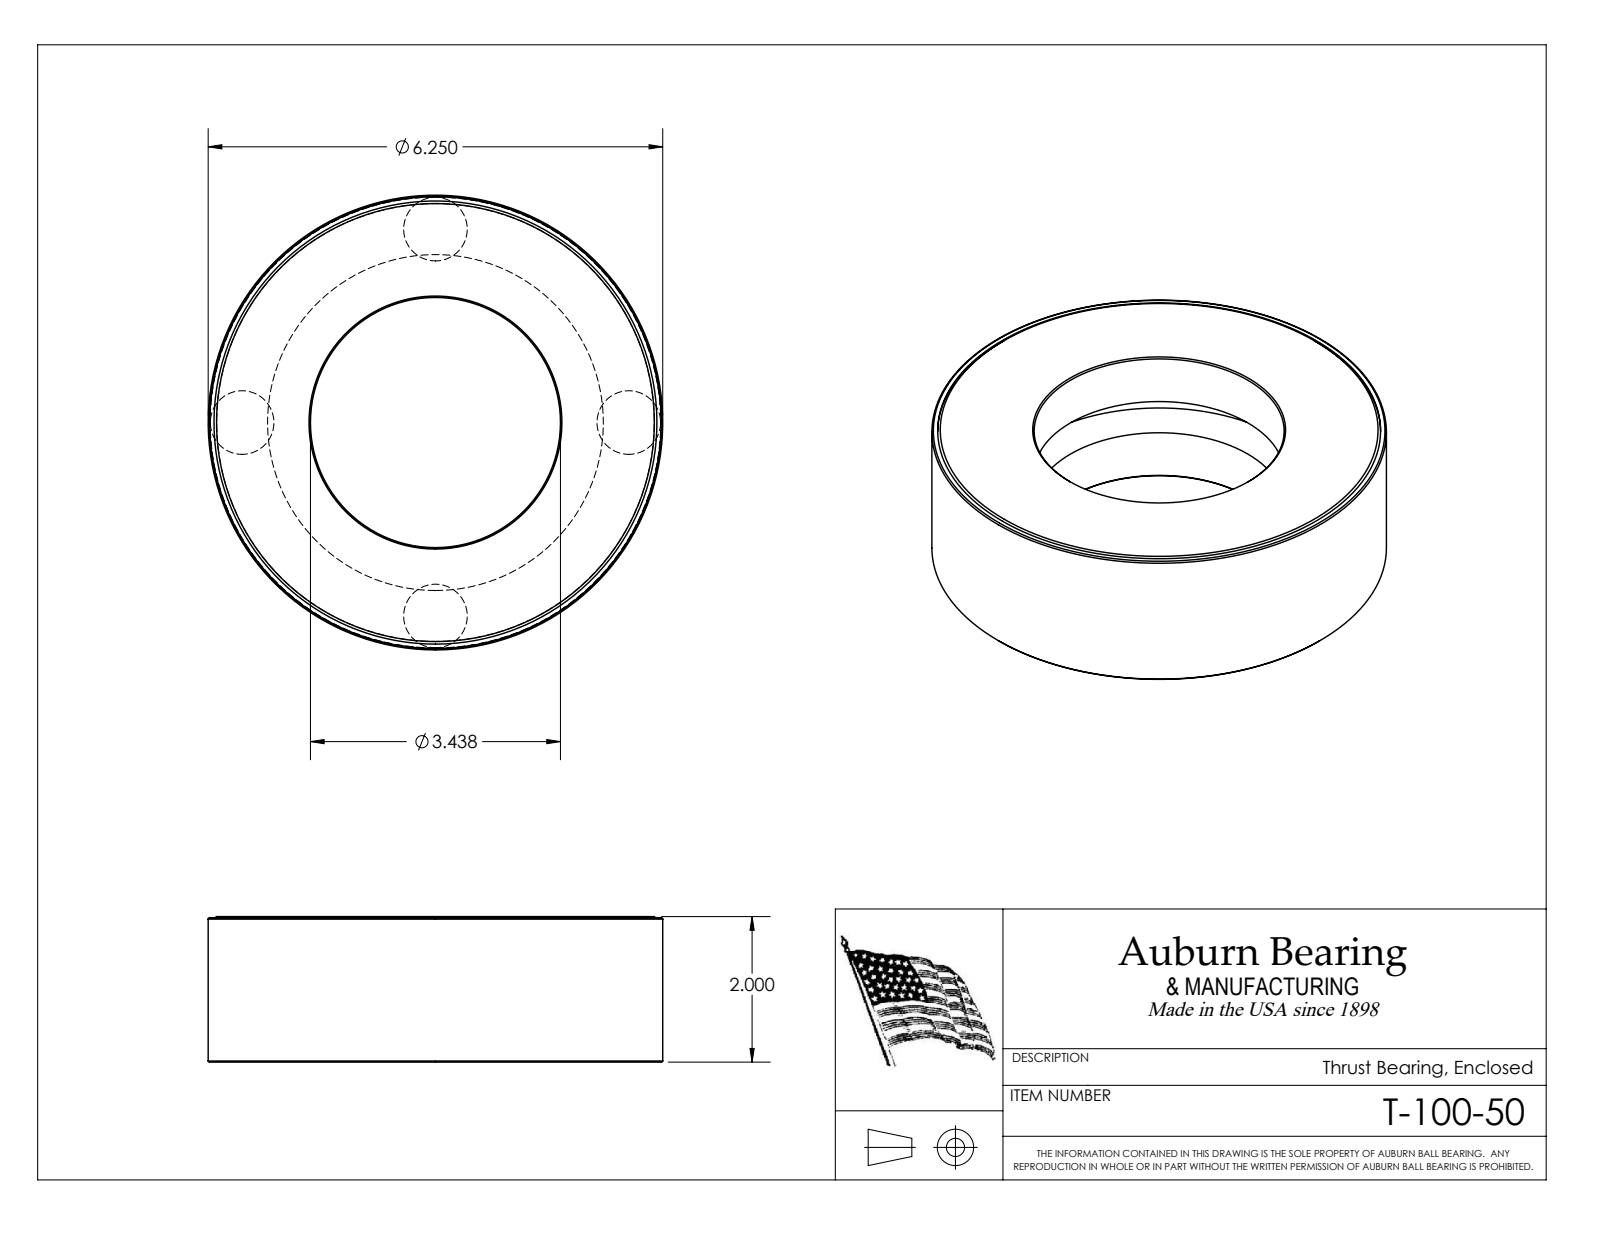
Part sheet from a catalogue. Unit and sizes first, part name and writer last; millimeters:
Units: millimetres
Overall size (bounding box): 158.8 × 158.8 × 50.8
Round holes (diameter × count): ⌀87.3 ×1, ⌀154.7 ×1, ⌀157.7 ×1
Round bosses / shafts (diameter × count): ⌀158.8 ×1, ⌀157.4 ×1
Main face-to-face distances: 50.8, 18.7, 32.1, 13.3, 49.9, 31.2, 17.8, 0.9, 50.4, 31.7
Volume: 494 100 mm³ · Surface area: 124 100 mm²
Bodies: 6 solids, 28 faces (9 planar, 7 cylindrical, 12 other)
Part name (STEP PRODUCT): T-100-50
STEP written by: SolidWorks 2016 (CONFIG_CONTROL_DESIGN)
